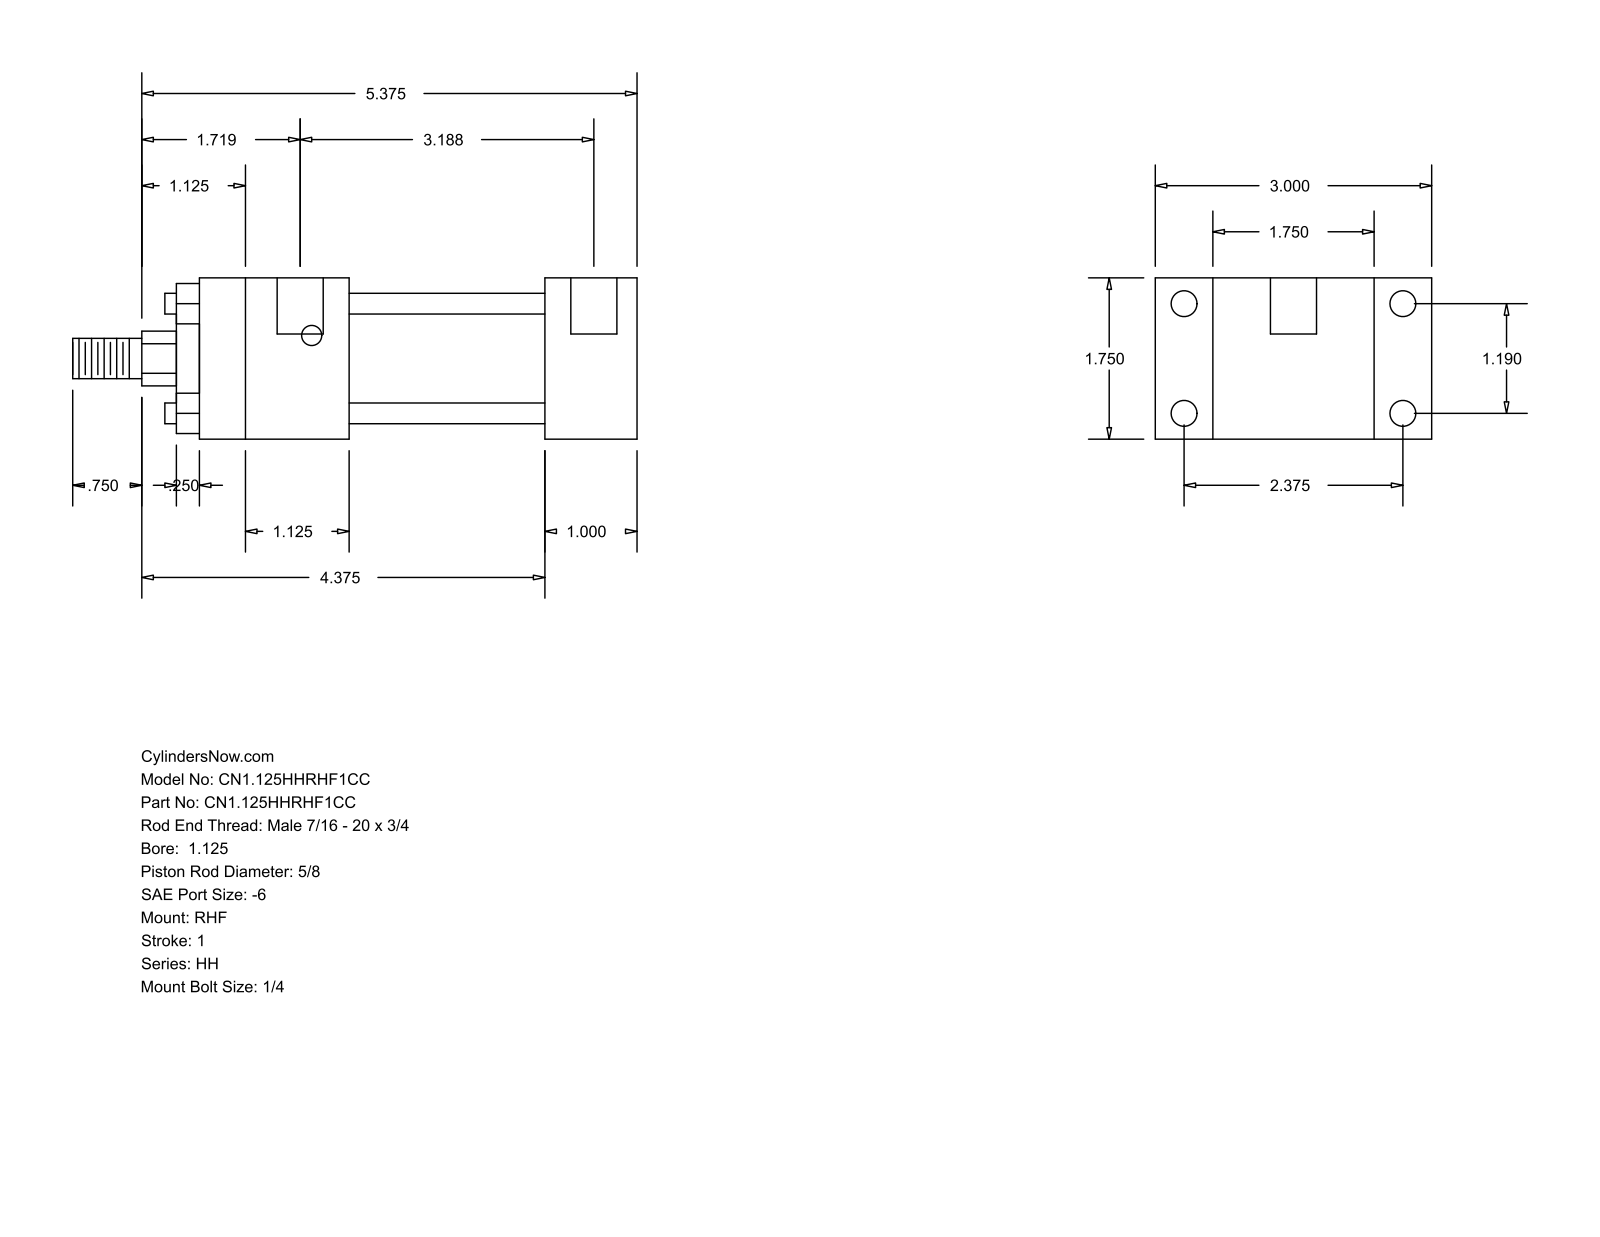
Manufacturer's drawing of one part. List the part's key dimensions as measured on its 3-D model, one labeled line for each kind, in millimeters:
Part name (STEP PRODUCT): HH_RHF__0112_0.625
STEP written by: GSSL Pune (CONFIG_CONTROL_DESIGN)
Units: millimetres
Bodies: 0 solids, 88 faces (60 planar, 28 cylindrical, 0 other)
Overall size (bounding box): 155.57 × 76.2 × 44.45
Round holes (diameter × count): ⌀5.56 ×4, ⌀7.14 ×4, ⌀12.7 ×2
Round bosses / shafts (diameter × count): ⌀5.71 ×4, ⌀34.92 ×1, ⌀28.57 ×1, ⌀15.88 ×1, ⌀11.11 ×1
Partial cylindrical surfaces — rounded edges, fillets, slot ends (radius × count): R7.54 ×1
Main face-to-face distances: 44.46, 15.87, 60.33, 25.41, 76.2, 53.97, 79.38, 41.27, 95.24, 120.65
Hole centre spacings: 30.22, 60.32, 67.47, 77.79, 3.17, 80.96
